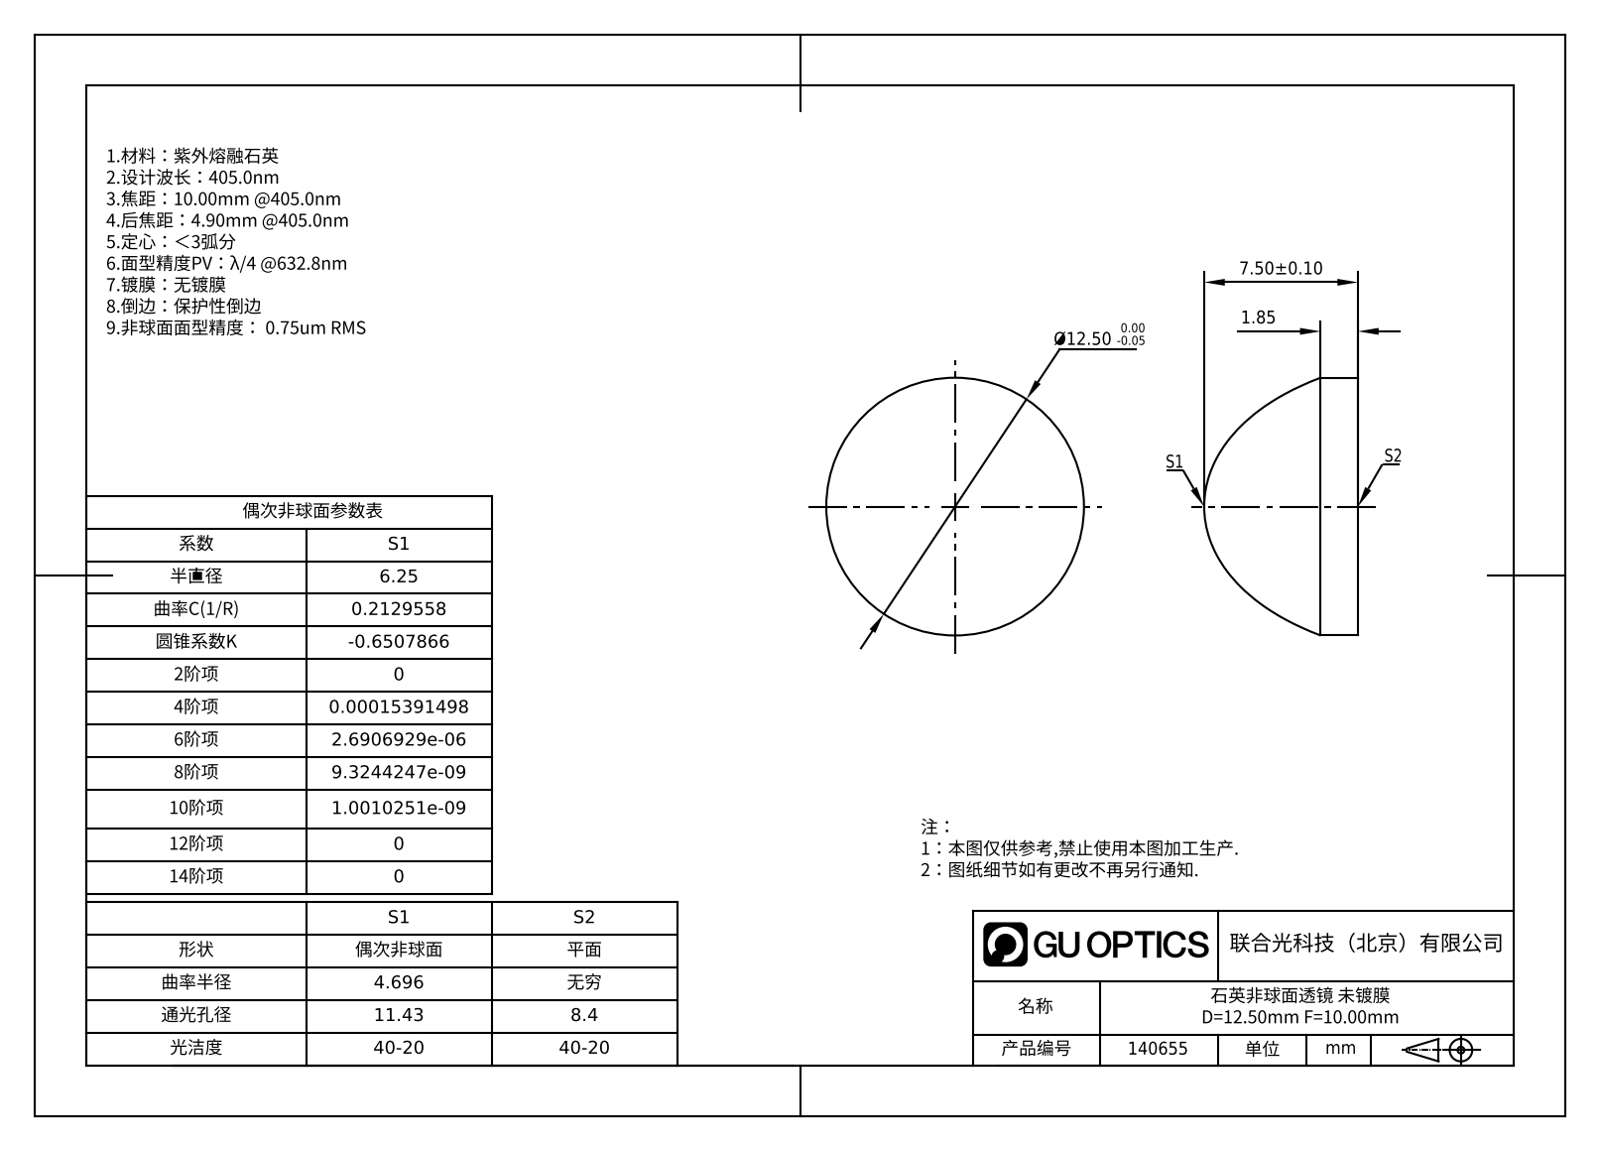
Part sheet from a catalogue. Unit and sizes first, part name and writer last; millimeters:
Units: millimetres
Overall size (bounding box): 12.5 × 12.5 × 7.5
Round bosses / shafts (diameter × count): ⌀12.5 ×1
Volume: 613 mm³ · Surface area: 402 mm²
Bodies: 1 solid, 5 faces (1 planar, 2 cylindrical, 2 other)
Part name (STEP PRODUCT): GASP21-012-010; GASP21-012-010.stp; surfaces 1,2.stp
STEP written by: SolidWorks 2023 (CONFIG_CONTROL_DESIGN)
